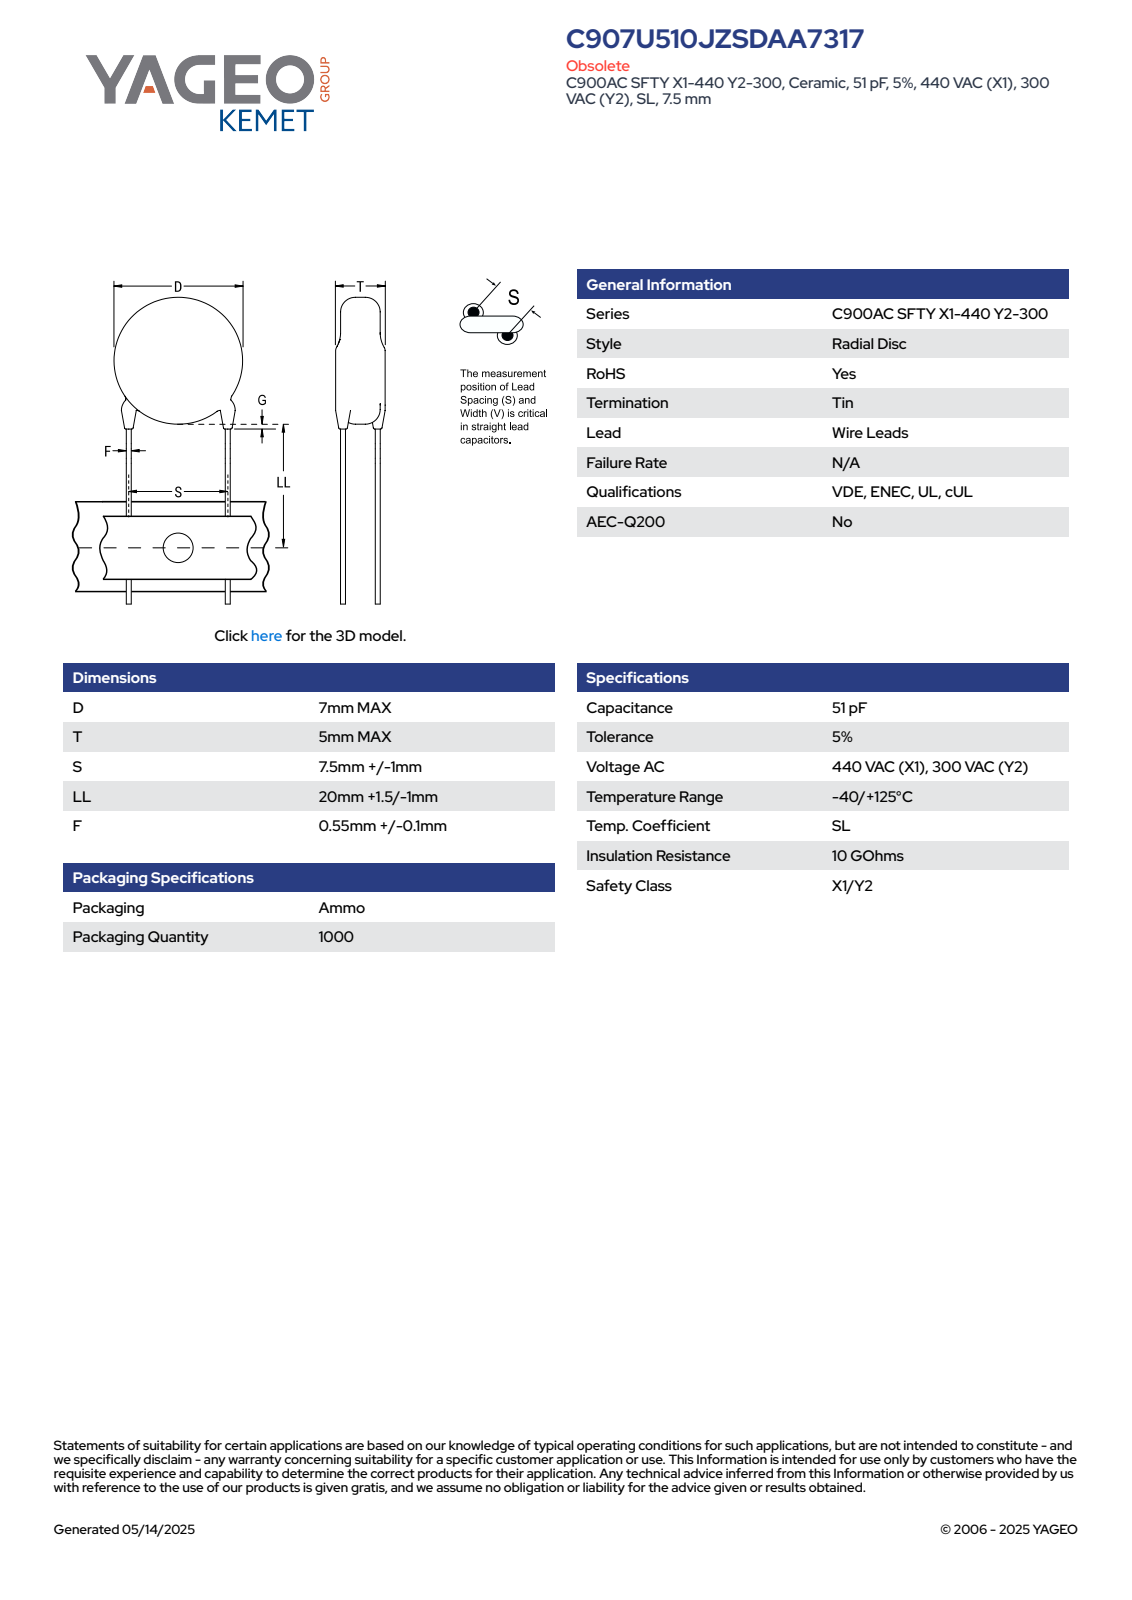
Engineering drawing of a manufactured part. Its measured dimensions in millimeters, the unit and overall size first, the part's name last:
Units: millimetres
Overall size (bounding box): 28.5 × 7.01 × 5.09
Round bosses / shafts (diameter × count): ⌀0.65 ×2, ⌀7 ×1
Main face-to-face distances: 5, 0.81, 25.4, 24.59, 3.3, 1.67, 3.52, 2.4, 2.49, 1.32
Volume: 200 mm³ · Surface area: 267 mm²
Bodies: 4 solids, 83 faces (61 planar, 6 cylindrical, 16 other)
Part name (STEP PRODUCT): CCD_STC900_D7T5S7.5LL21.5F0.65G3
STEP written by: SolidWorks 2014 (AUTOMOTIVE_DESIGN)
